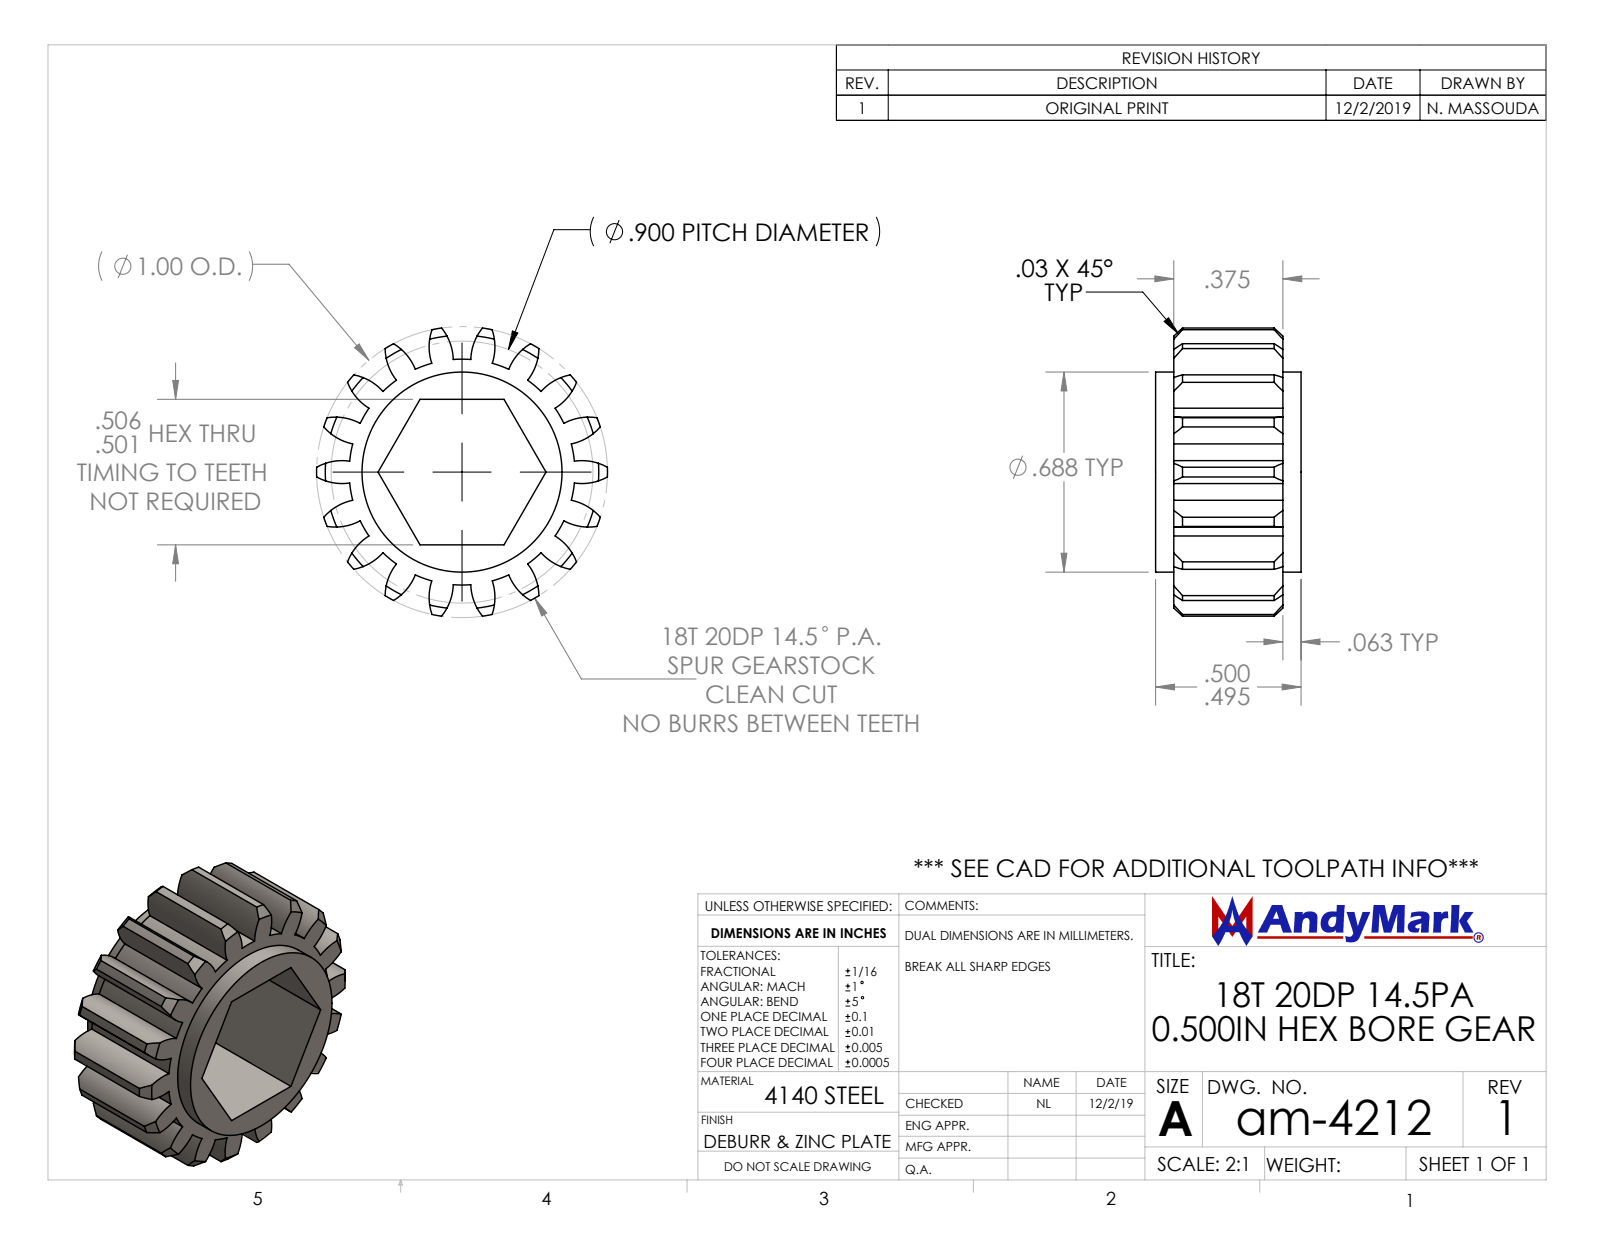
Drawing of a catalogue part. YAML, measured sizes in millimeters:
part_name: "am-4212 18T 20DP 500hex 375 FW"
step_written_by: "SolidWorks 2019 (CONFIG_CONTROL_DESIGN)"
units: millimeters
bodies: {solids: 1, faces: 143, planar: 10, cylindrical: 79, other: 54}
overall_size: [25.4, 25.1, 12.7]
volume: 2720
surface_area: 2638
round_bosses_or_shafts:
  - {diameter: 17.4, count: 1}
partial_cylinders:
  - {radius: 4.6, count: 36}
  - {radius: 9.9, count: 1}
  - {radius: 12.7, count: 1}
face_to_face_distances: [12.7, 9.5, 1.6, 11.1, 11.1, 1.6]
